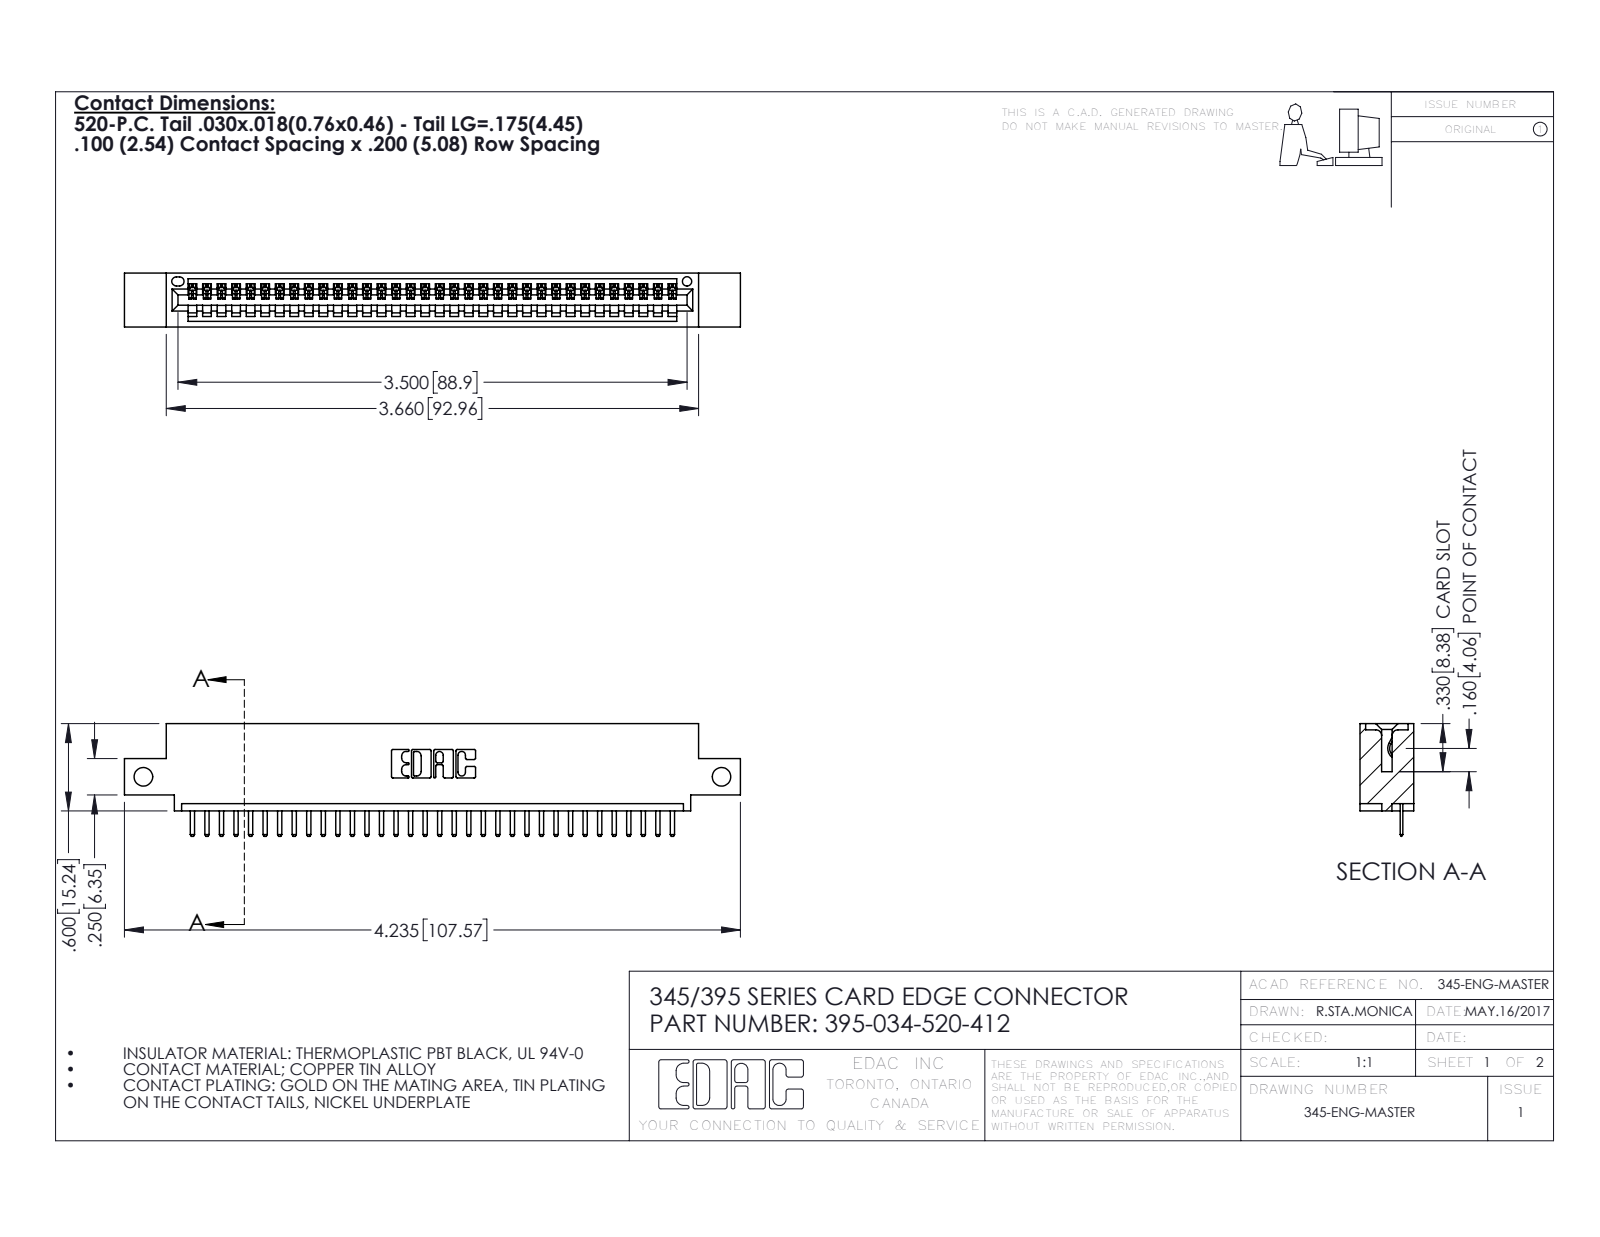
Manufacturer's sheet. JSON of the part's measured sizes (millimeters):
{"part_name": "395-034-520-412; 345 Part_0.110 Offset - Side Mount; 345-292-001_345-293-120", "step_written_by": "SolidWorks 2016 (CONFIG_CONTROL_DESIGN)", "units": "millimeters", "bodies": {"solids": 35, "faces": 2238, "planar": 1512, "cylindrical": 726, "other": 0}, "overall_size": [107.6, 19.7, 9.4], "volume_mm3": 9900, "surface_area_mm2": 12660, "round_holes": [[3.3, 2], [1.6, 1]], "partial_cylinders_radius": [[0.3, 70], [0.2, 68], [0.3, 22], [0.2, 6], [0.8, 6], [0.7, 3], [0.8, 2], [1, 2]], "face_to_face_distances": [7.6, 1.8, 9.4, 5.1, 2.5, 6.9, 0.6, 5.7, 1.8, 3.8], "hole_center_spacings": [101]}
